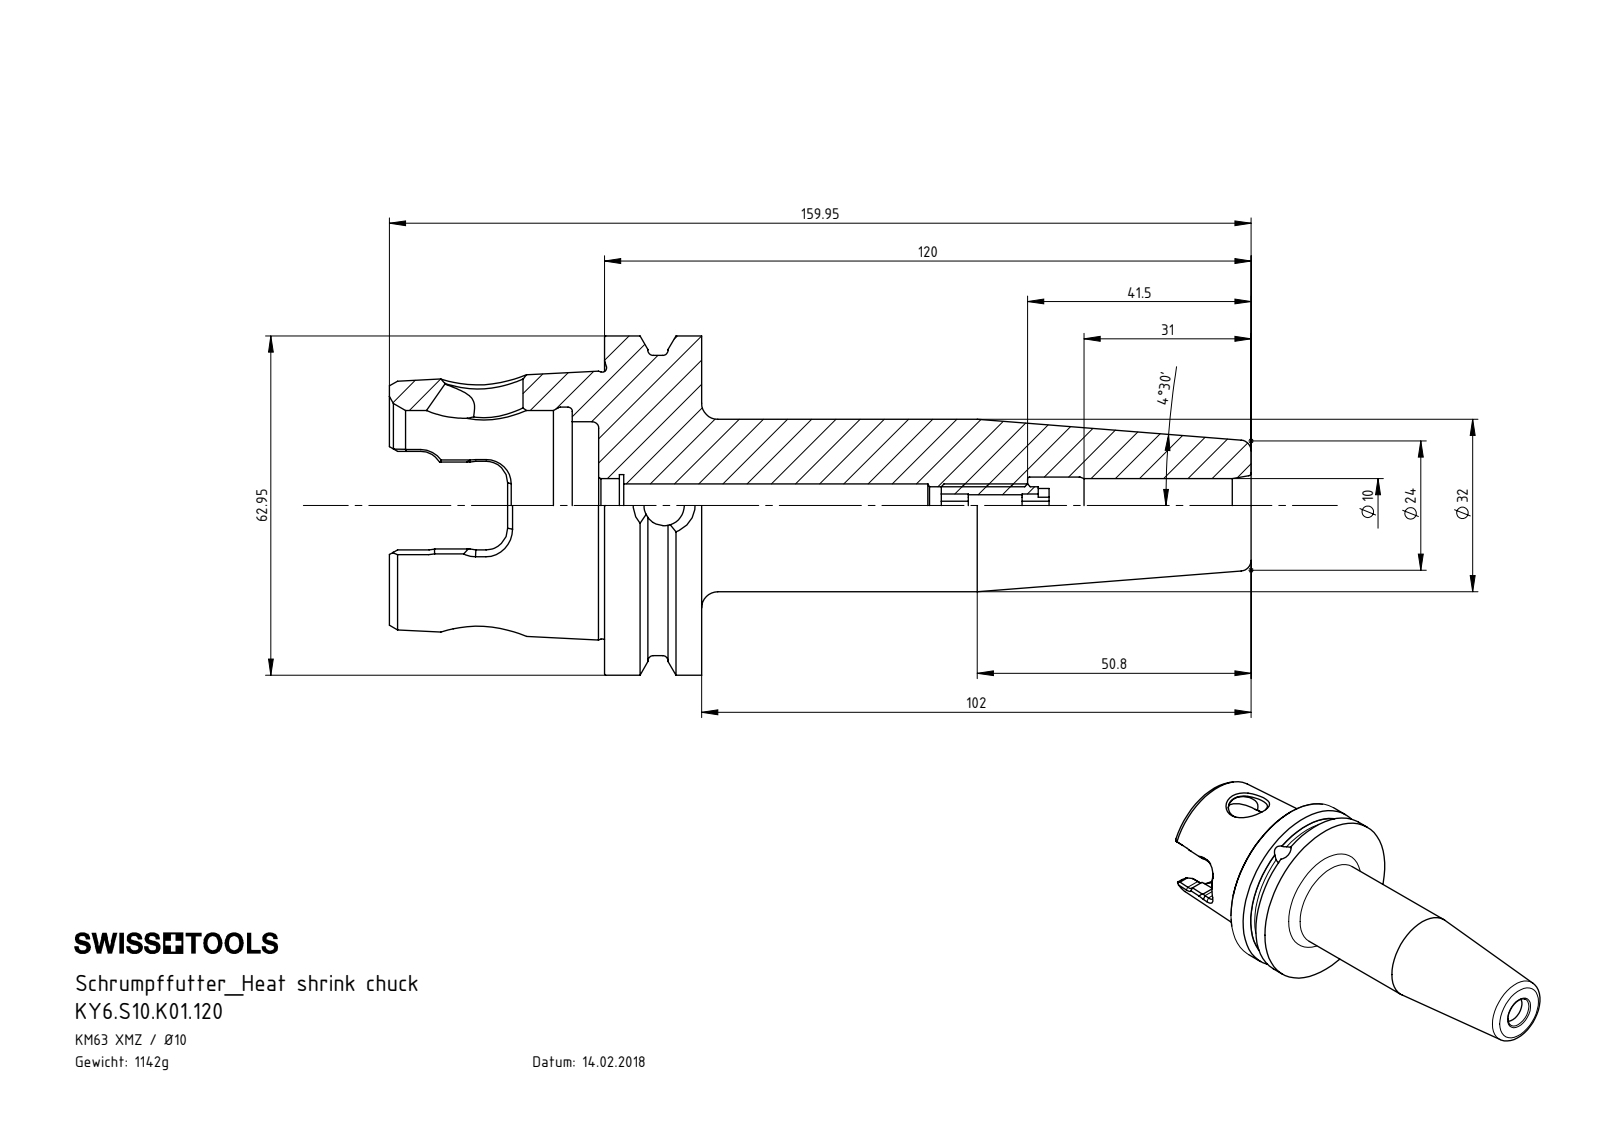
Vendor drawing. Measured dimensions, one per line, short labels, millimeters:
name: KY6.S10.K01.120; KY6-S10.K01.120_A; ERU-AN3.K01.020_A
written by: SolidWorks 2017 (CONFIG_CONTROL_DESIGN)
unit: mm
bodies: 2 solids, 272 faces (79 planar, 60 cylindrical, 133 other)
size: 159.95 × 62.95 × 62.95
volume: 145 467 mm³; area: 32 853 mm²
holes: 2× ⌀7.47, 1× ⌀4, 1× ⌀7, 1× ⌀8, 1× ⌀8.48, 1× ⌀10, 1× ⌀10.6, 1× ⌀11.5, 1× ⌀14.5, 1× ⌀31.1, 1× ⌀35.27, 1× ⌀36.5
bosses: 1× ⌀62.95, 1× ⌀55.7, 1× ⌀32
rounds: 6× R4, 2× R7.04
face distances: 18, 1.1, 19.1, 121.1, 120, 102, 4.9, 6, 24, 126
